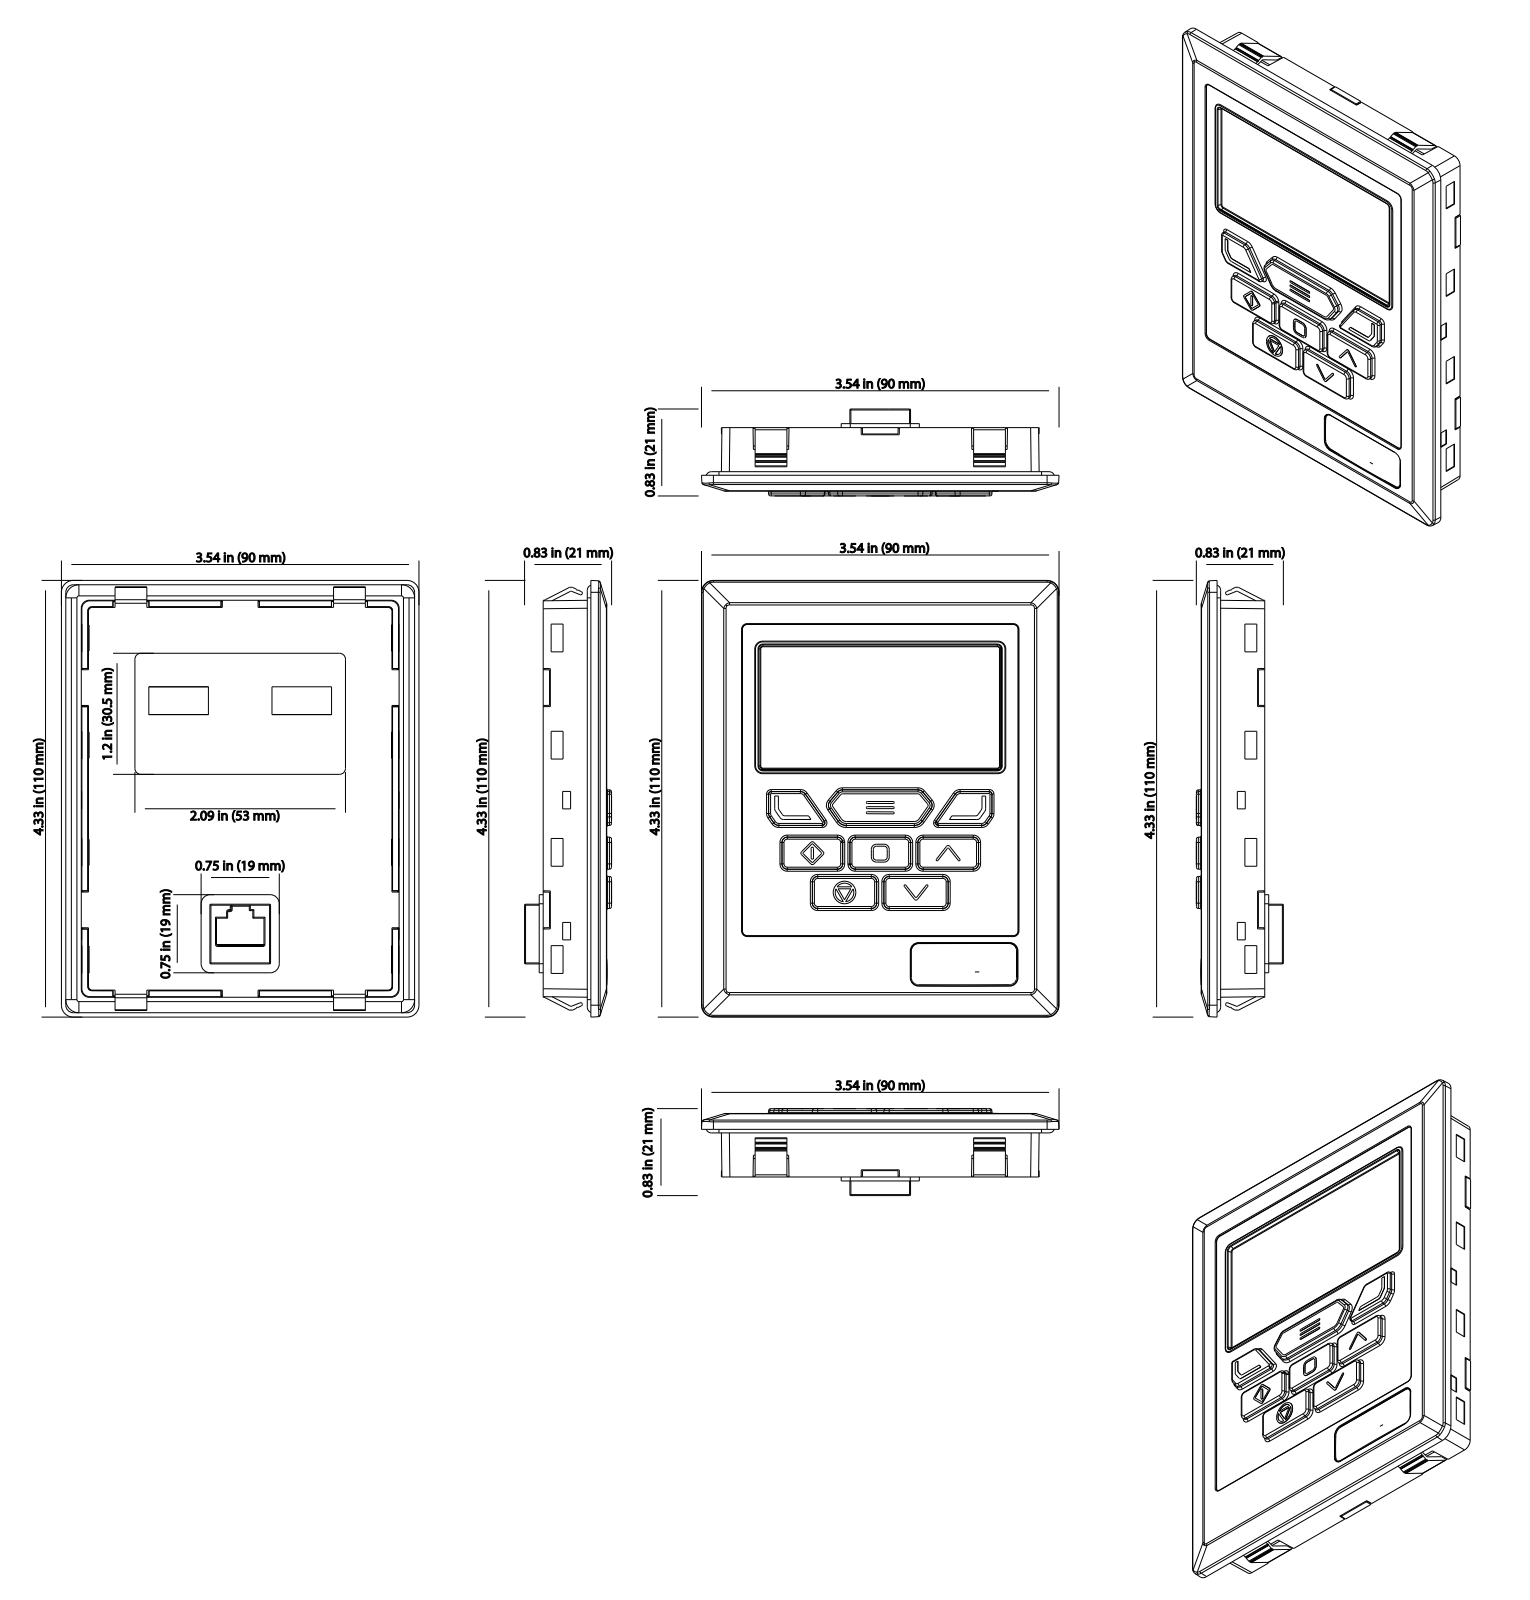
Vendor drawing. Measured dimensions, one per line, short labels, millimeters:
name: OptiPAD.TFT (ENVELOPE)
written by: SolidWorks 2022 (CONFIG_CONTROL_DESIGN)
unit: mm
bodies: 1 solid, 954 faces (472 planar, 197 cylindrical, 285 other)
size: 110 × 90 × 21.91
volume: 131 917 mm³; area: 28 277 mm²
rounds: 36× R0.5, 25× R0.25, 16× R0.2, 12× R0.24, 12× R2, 8× R0.1, 8× R1, 4× R0.15
face distances: 15.7, 16, 14.85, 0.85, 1.15, 14.65, 15.5, 15.8, 1.2, 17
